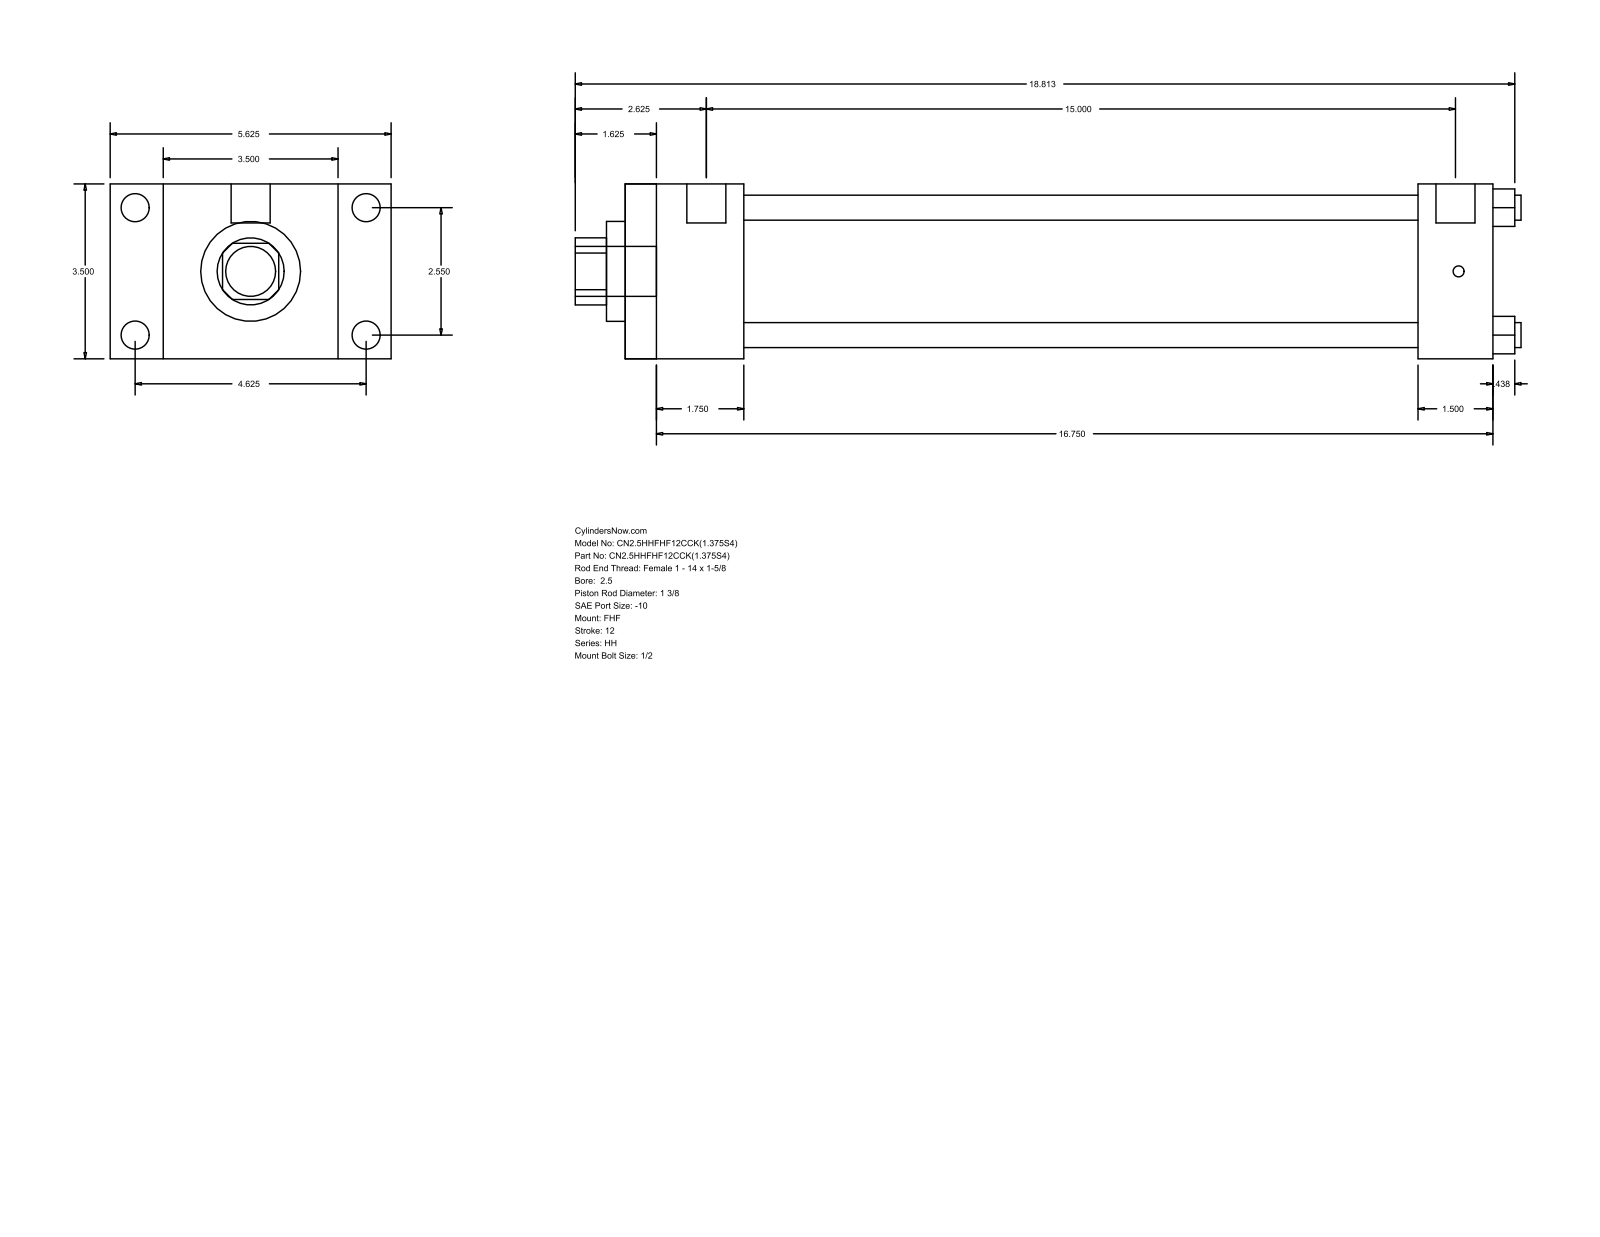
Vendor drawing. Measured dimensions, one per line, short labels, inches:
name: HH_FHF__0250_1.375
written by: GSSL Pune (CONFIG_CONTROL_DESIGN)
unit: in
bodies: 0 solids, 88 faces (60 planar, 28 cylindrical, 0 other)
size: 18.937 × 5.625 × 3.5
holes: 4× ⌀0.5, 1× ⌀1.375, 1× ⌀2, 1× ⌀2.875
bosses: 4× ⌀0.563, 4× ⌀0.219, 2× ⌀0.781, 1× ⌀1
rounds: 1× R0.672
face distances: 3.5, 2.375, 1.063, 4.563, 17.375, 15, 5.625, 15.875, 13.5, 1.5
hole spacings: 1.803, 2.55, 3.606
